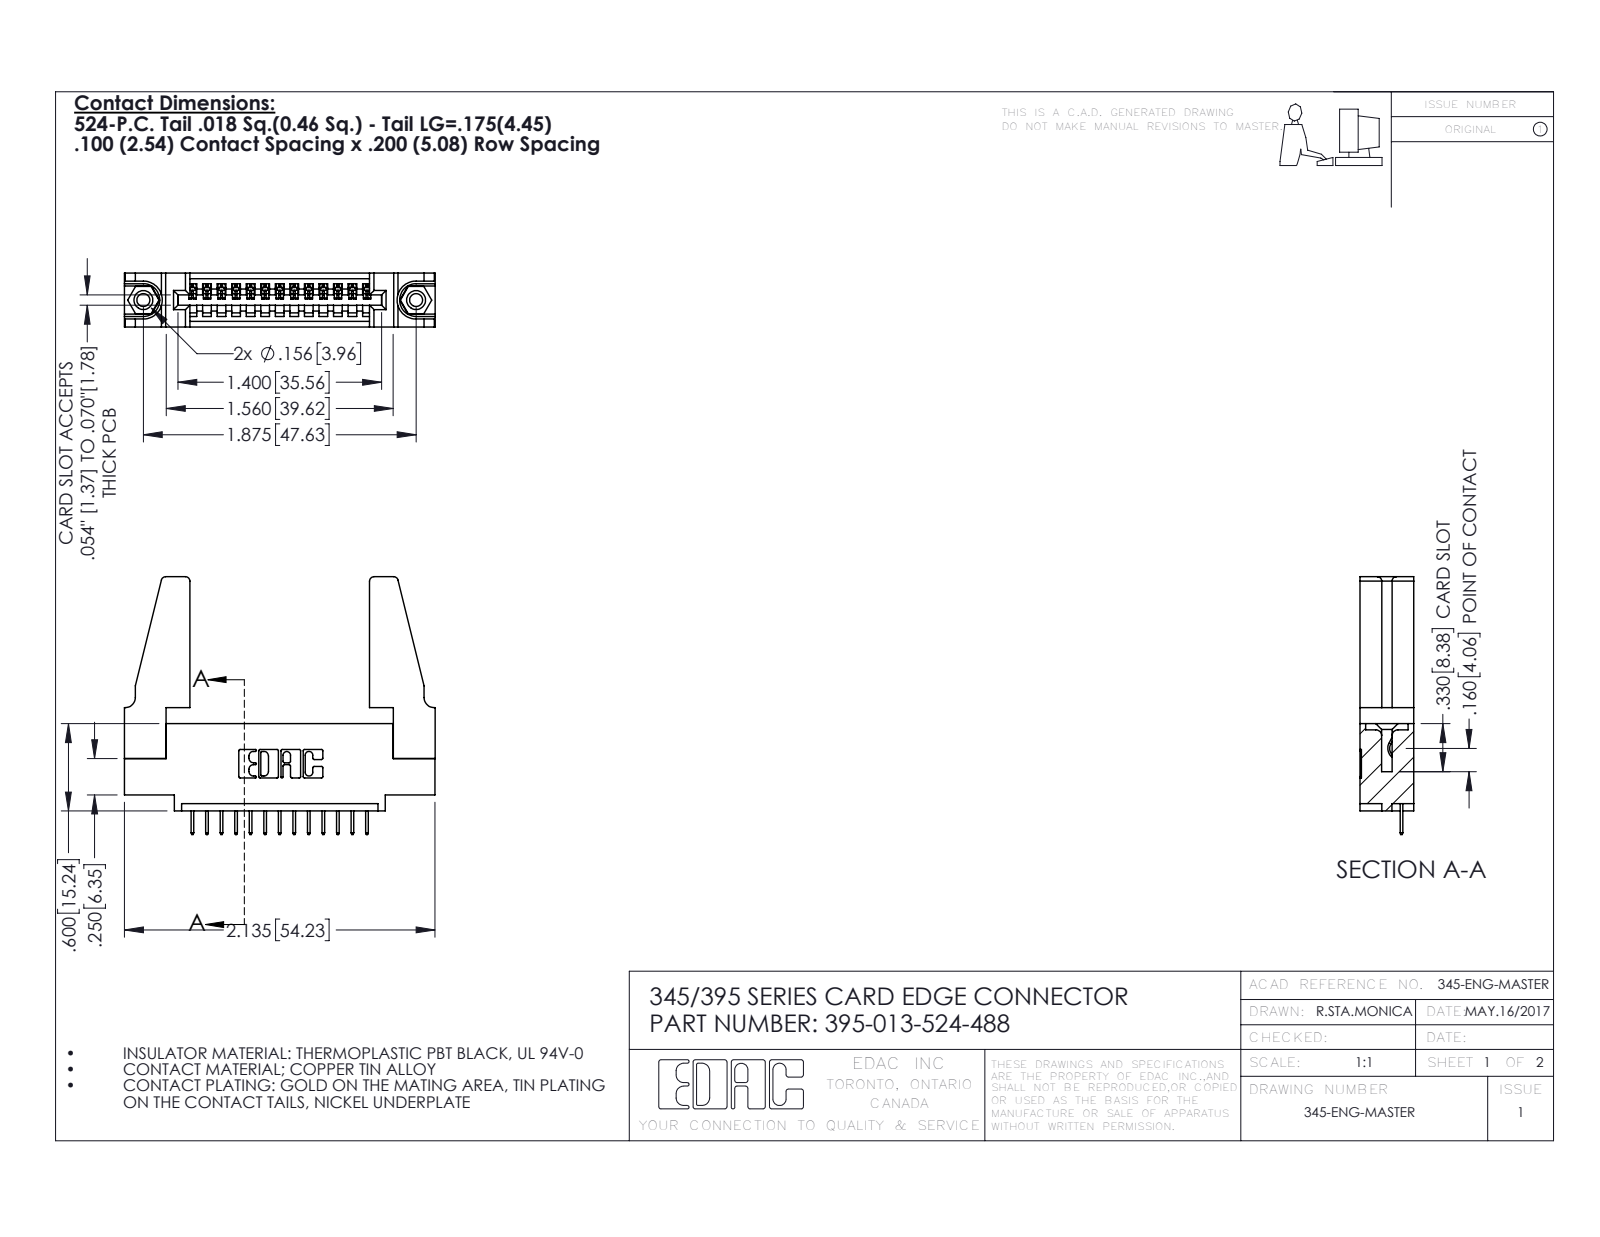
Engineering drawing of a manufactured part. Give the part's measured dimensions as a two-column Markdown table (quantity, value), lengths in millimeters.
| quantity | value |
| --- | --- |
| part name | 395-013-524-488; 345-220-078_345-220-088; 345 Part_0.110 Offset - 0.156 Dia-TH; 345-250-001_345-250-001-102 (+1 more) |
| STEP written by | SolidWorks 2016 (CONFIG_CONTROL_DESIGN) |
| units | millimeters |
| bodies | 18 solids, 1060 faces (754 planar, 290 cylindrical, 16 other) |
| overall size | 54.3 × 45 × 9.4 |
| volume | 8 050 mm³ |
| surface area | 9 019 mm² |
| round holes (diameter × count) | 2.3 × 2, 3.2 × 2, 4 × 2, 1.6 × 1 |
| round bosses / shafts (diameter × count) | 3.9 × 2 |
| partial cylindrical surfaces (radius × count) | 0.2 × 26, 0.3 × 22, 0.8 × 8, 0.2 × 6, 0.8 × 6, 0.7 × 3, 0.8 × 2, 1 × 2 |
| main face-to-face distances | 9.4, 1.8, 7.6, 5.1, 2.5, 6.9, 0.6, 5.7, 3.8, 3.8 |
| hole center spacings | 6.9, 41.7, 47.6 |
